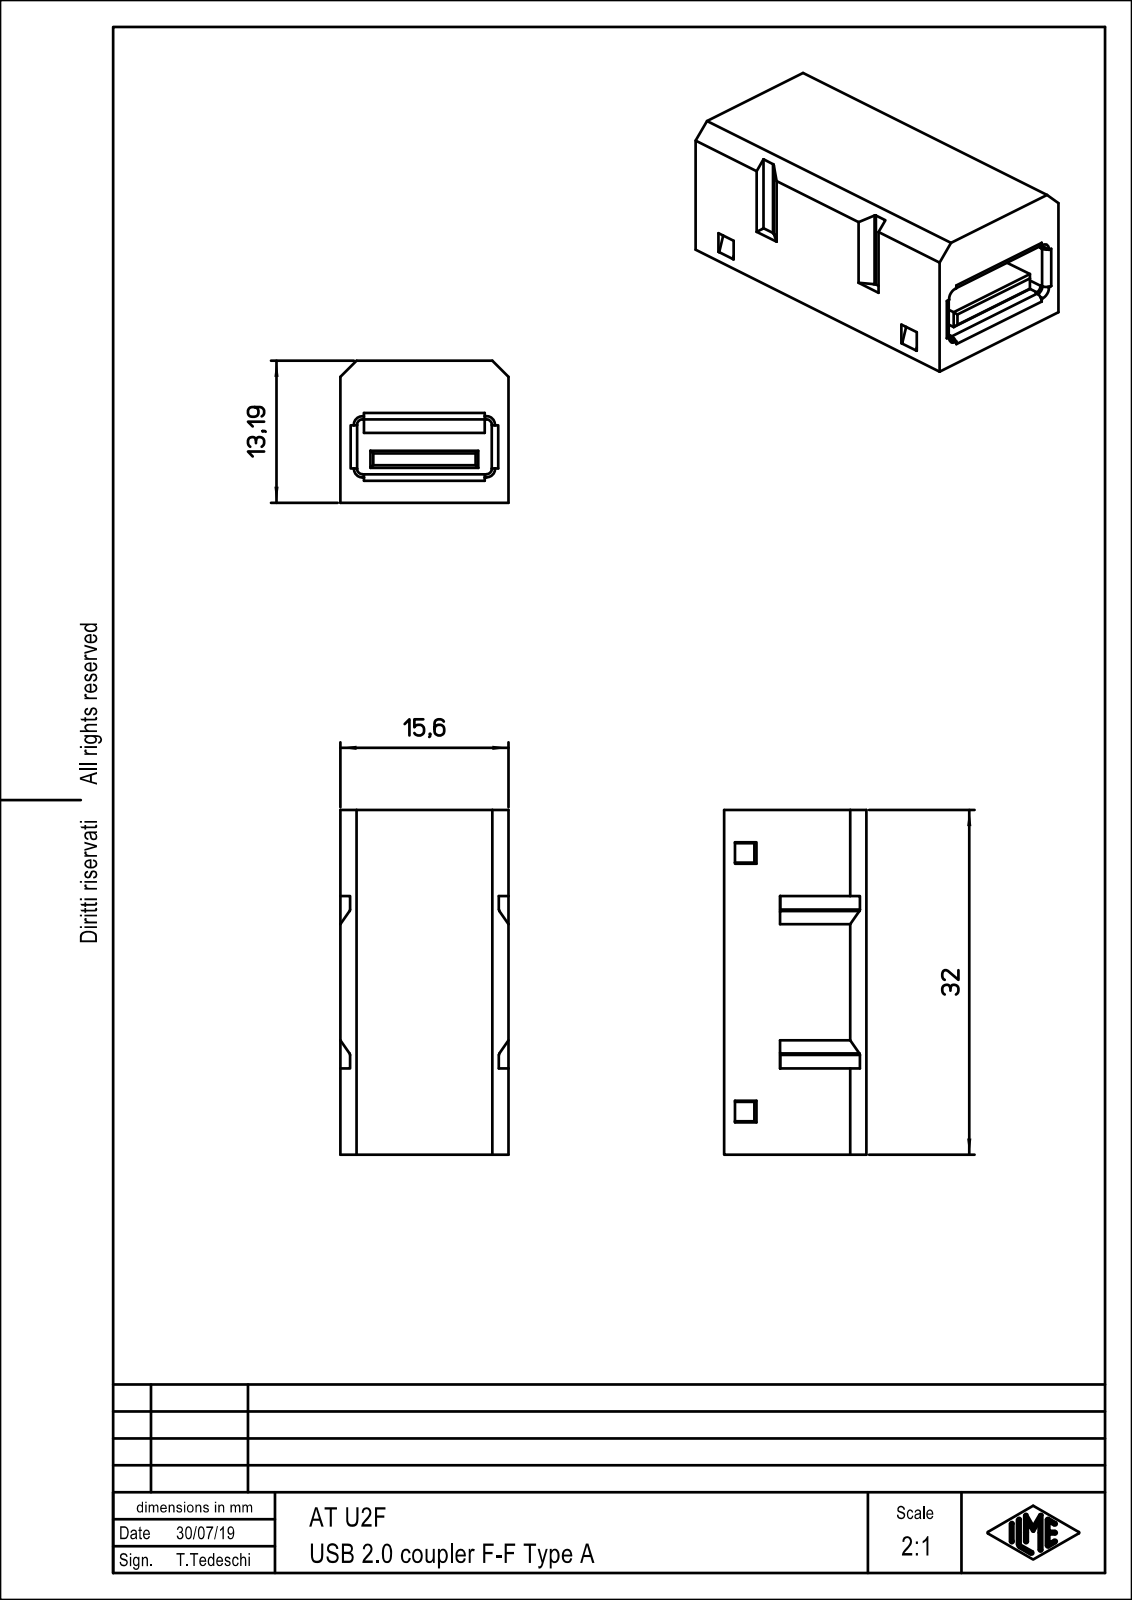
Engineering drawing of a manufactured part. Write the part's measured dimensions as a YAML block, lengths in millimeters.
part_name: "AF_U2F"
step_written_by: "Creo Elements/Direct Modeling 20.1B 02-Apr-2019 (C) Parametric Technology GmbH (AUTOMOTIVE_DESIGN)"
units: millimeters
bodies: {solids: 1, faces: 196, planar: 166, cylindrical: 30, other: 0}
overall_size: [32, 15.6, 13.19]
volume: 5143
surface_area: 3939
partial_cylinders:
  - {radius: 0.6, count: 8}
  - {radius: 0.25, count: 4}
  - {radius: 0.5, count: 4}
  - {radius: 0.8, count: 4}
  - {radius: 0.3, count: 2}
face_to_face_distances: [13.19, 15.6, 10.55, 2.64, 5.45, 5.1, 7.74, 2.2, 0.6, 1.6]
